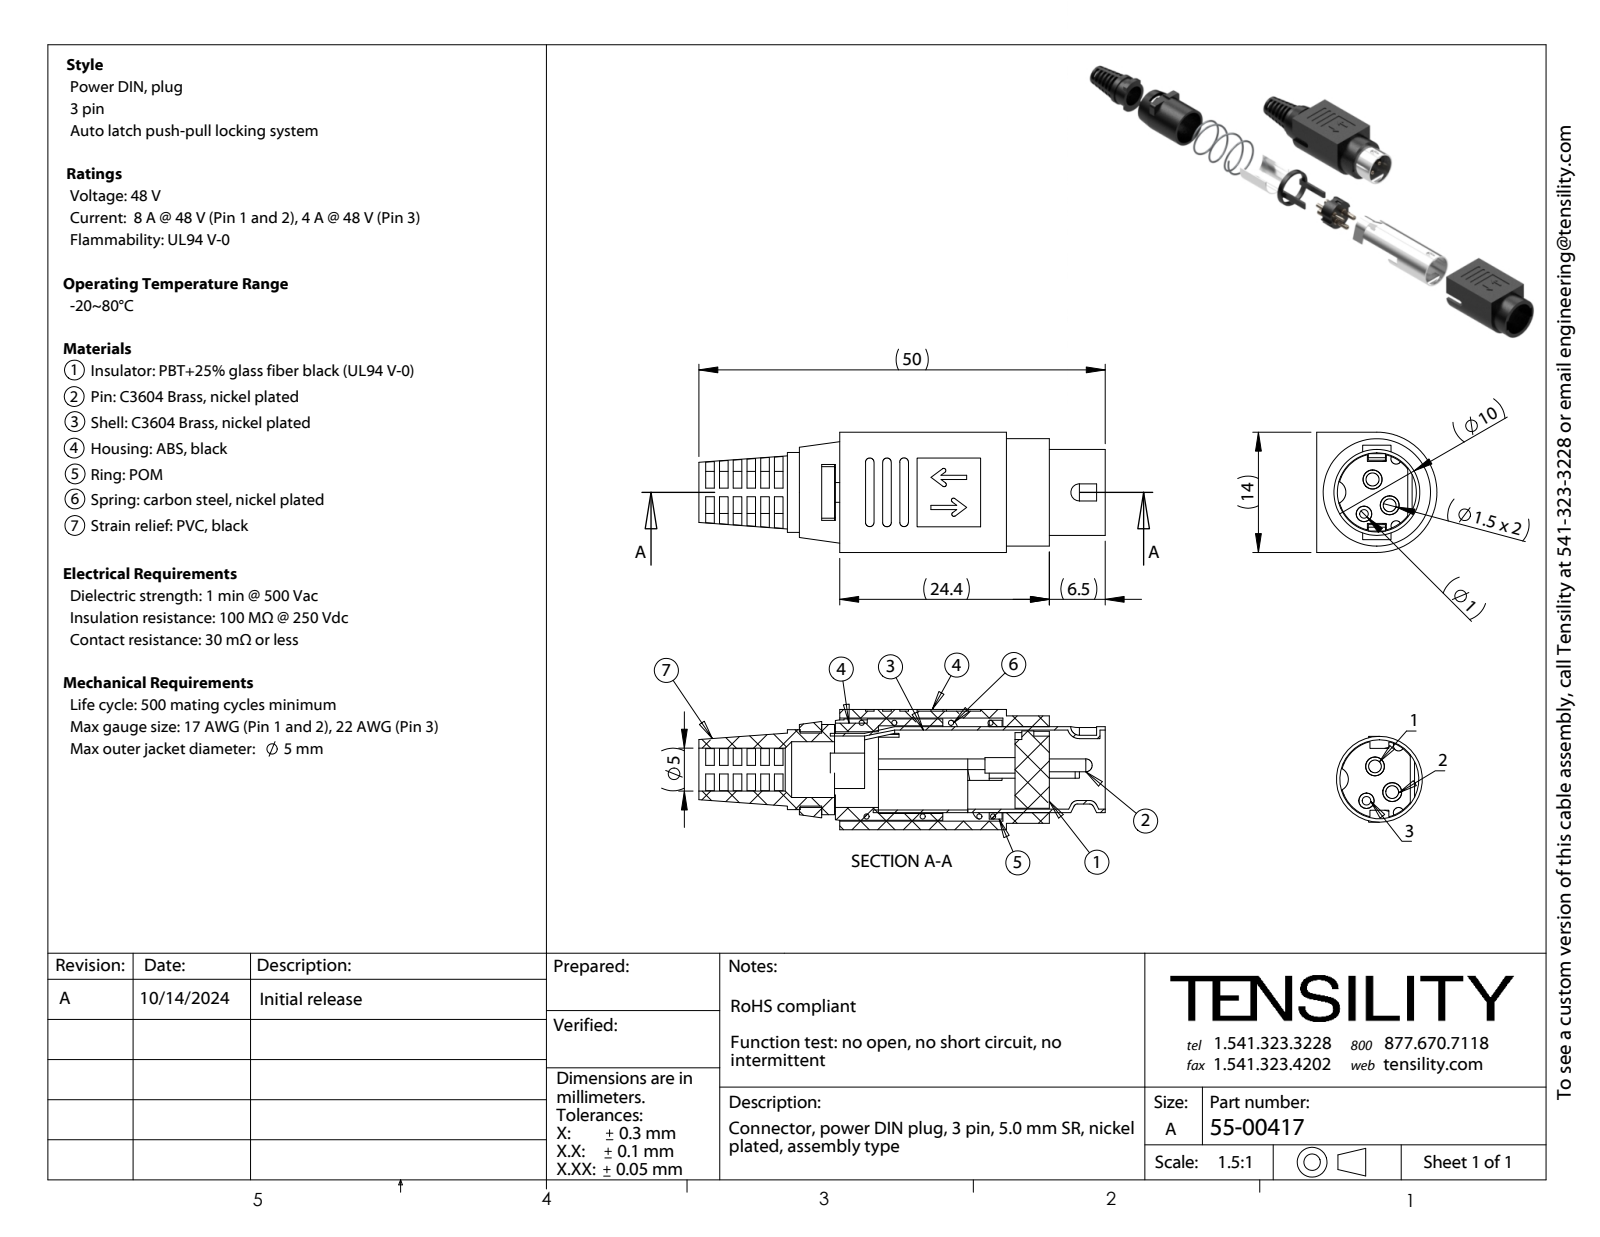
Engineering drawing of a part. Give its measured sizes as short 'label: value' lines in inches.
name: 55-00417-05_默认; 55-00417-10_默认; 55-00417-03_默认; 55-00417-01_默认 (+7 more)
written by: SolidWorks 2025 (CONFIG_CONTROL_DESIGN)
unit: in
bodies: 11 solids, 403 faces (266 planar, 111 cylindrical, 26 other)
size: 1.862 × 0.551 × 0.551
volume: 0.163 in³; area: 11.44 in²
holes: 2× ⌀0.047, 1× ⌀0.028, 1× ⌀0.197, 1× ⌀0.256, 1× ⌀0.346, 1× ⌀0.362, 1× ⌀0.394, 1× ⌀0.402
bosses: 3× ⌀0.071, 2× ⌀0.087, 2× ⌀0.059, 1× ⌀0.492, 1× ⌀0.465, 1× ⌀0.453, 1× ⌀0.366, 1× ⌀0.354
rounds: 8× R0.02, 4× R0.039, 3× R0.024, 2× R0.01, 2× R0.01, 2× R0.035, 1× R0.055, 1× R0.059
face distances: 0.039, 0.512, 0.059, 0.063, 0.02, 0.472, 0.197, 0.217, 0.276, 0.024
hole spacings: 0.062, 0.083, 0.115, 0.124, 0.142, 0.162
